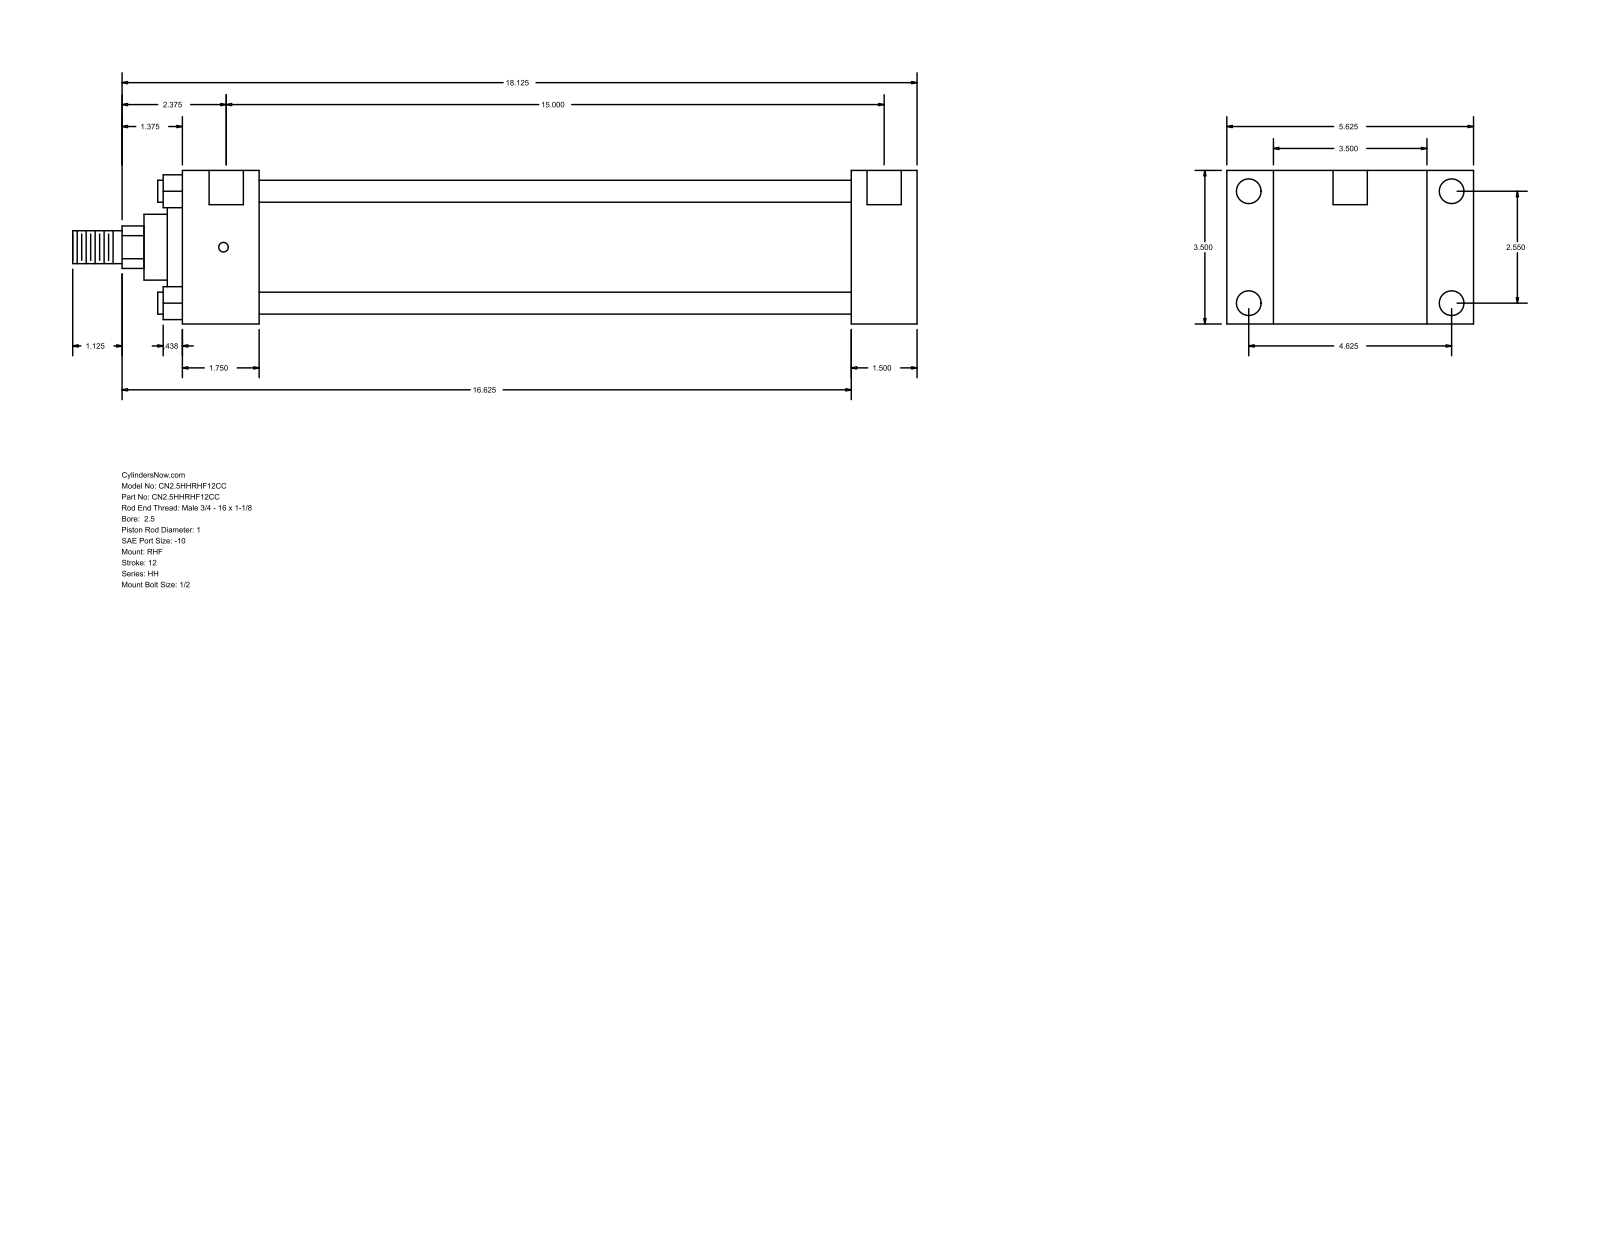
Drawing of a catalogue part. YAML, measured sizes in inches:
part_name: "HH_RHF__0250_1"
step_written_by: "GSSL Pune (CONFIG_CONTROL_DESIGN)"
units: inches
bodies: {solids: 0, faces: 90, planar: 61, cylindrical: 29, other: 0}
overall_size: [19.25, 5.625, 3.5]
round_holes:
  - {diameter: 0.219, count: 4}
  - {diameter: 0.563, count: 4}
  - {diameter: 0.781, count: 2}
round_bosses_or_shafts:
  - {diameter: 0.5, count: 4}
  - {diameter: 2.875, count: 1}
  - {diameter: 2.375, count: 1}
  - {diameter: 1.5, count: 1}
  - {diameter: 1, count: 1}
  - {diameter: 0.75, count: 1}
partial_cylinders:
  - {radius: 0.484, count: 1}
face_to_face_distances: [3.5, 1.5, 1.063, 4.563, 15.25, 16.75, 5.625, 1.75, 13.5, 15]
hole_center_spacings: [0.063, 2.55, 4.625, 5.281, 15.062, 15.125, 15]
